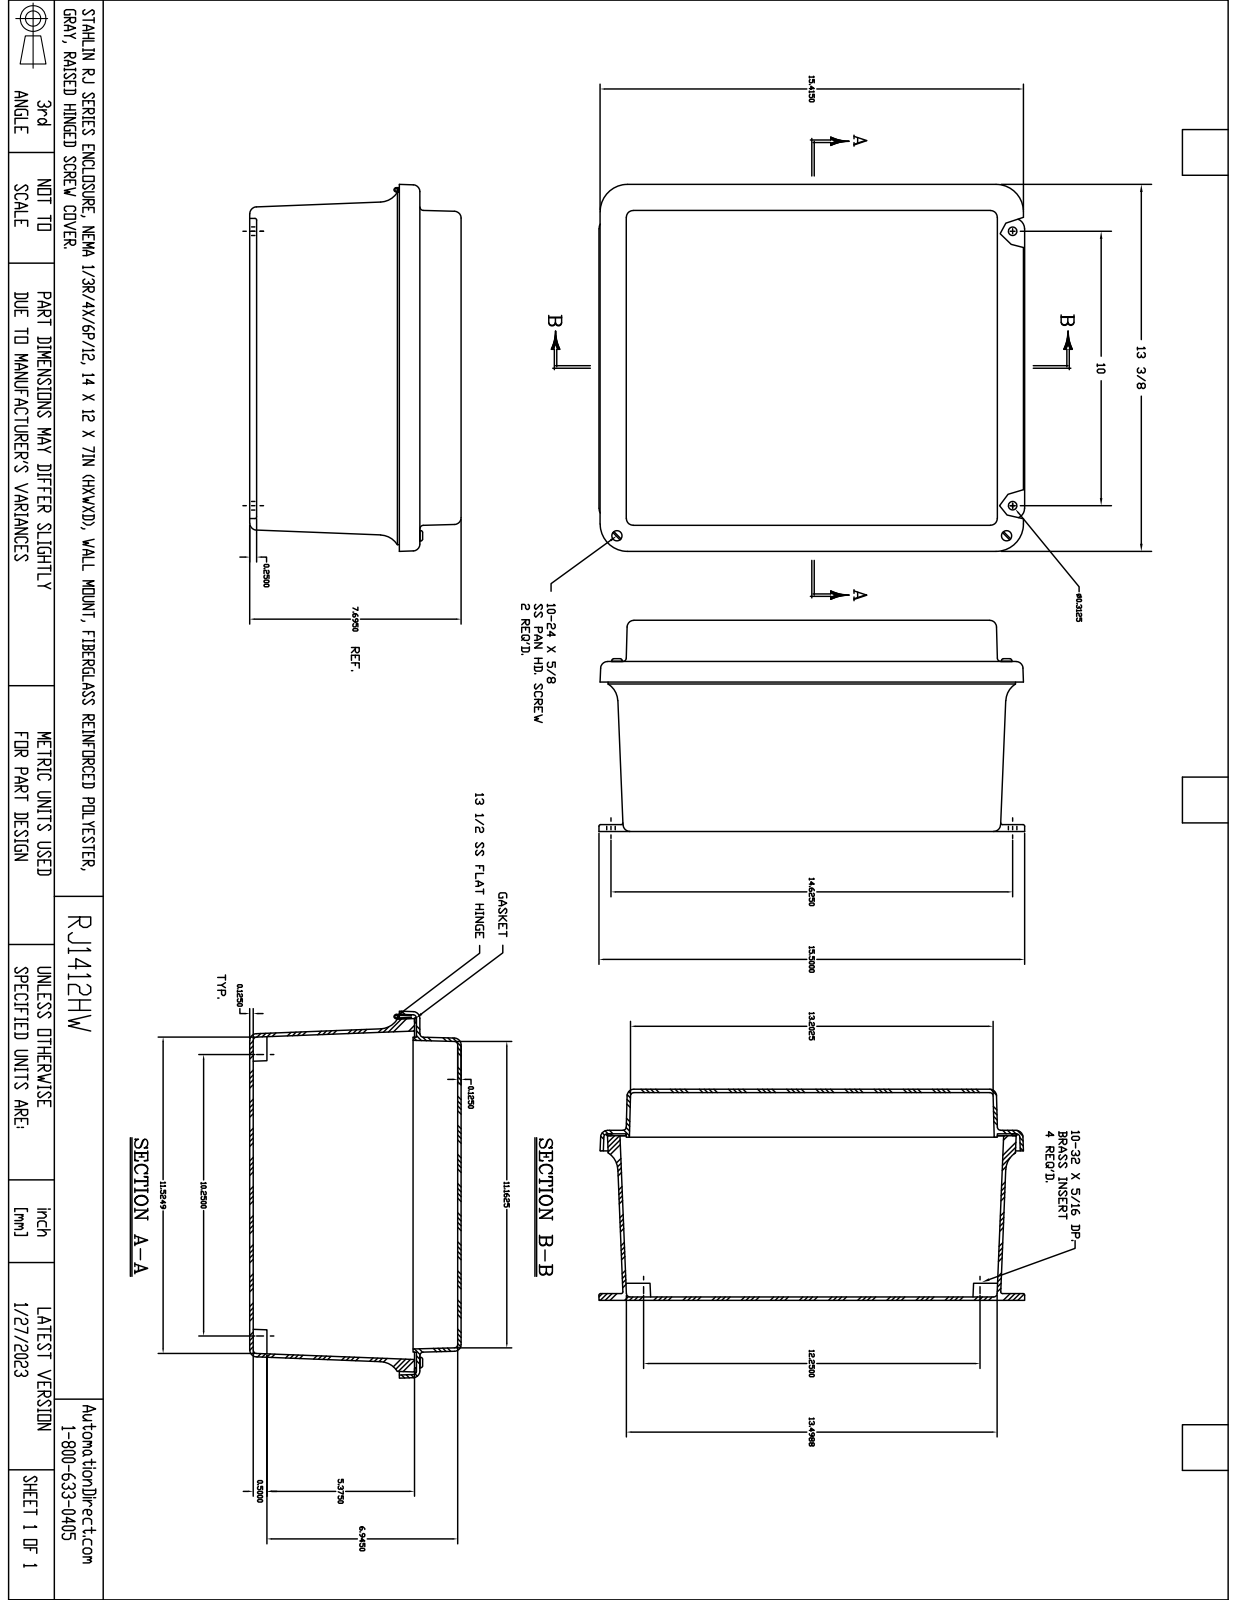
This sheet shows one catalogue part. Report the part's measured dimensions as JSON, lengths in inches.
{"part_name": "MR1412HW", "step_written_by": "SolidWorks 2018 (AUTOMOTIVE_DESIGN)", "units": "inches", "bodies": {"solids": 24, "faces": 925, "planar": 340, "cylindrical": 354, "other": 231}, "overall_size": [15.5, 13.403, 7.703], "volume_in3": 118.8, "surface_area_in2": 1711, "round_holes": [[0.131, 10], [0.14, 10], [0.152, 8], [0.156, 4], [0.218, 4], [0.145, 2], [0.085, 1], [0.085, 1]], "round_bosses_or_shafts": [[0.25, 10], [0.27, 6], [0.125, 6], [0.125, 4], [0.19, 2], [0.156, 2], [0.155, 1], [0.155, 1]], "partial_cylinders_radius": [[0.031, 20], [0.125, 20], [0.25, 20], [0.2, 4], [0.283, 4], [0.375, 4], [0.75, 4], [0.063, 2]], "face_to_face_distances": [0.125, 0.125, 7.453, 7.578, 7.703, 7.578, 1.5, 5.953, 6.078, 1.625], "hole_center_spacings": [3.25, 6.5, 9.75, 0.25, 3, 1.37, 6.25, 11.26]}
